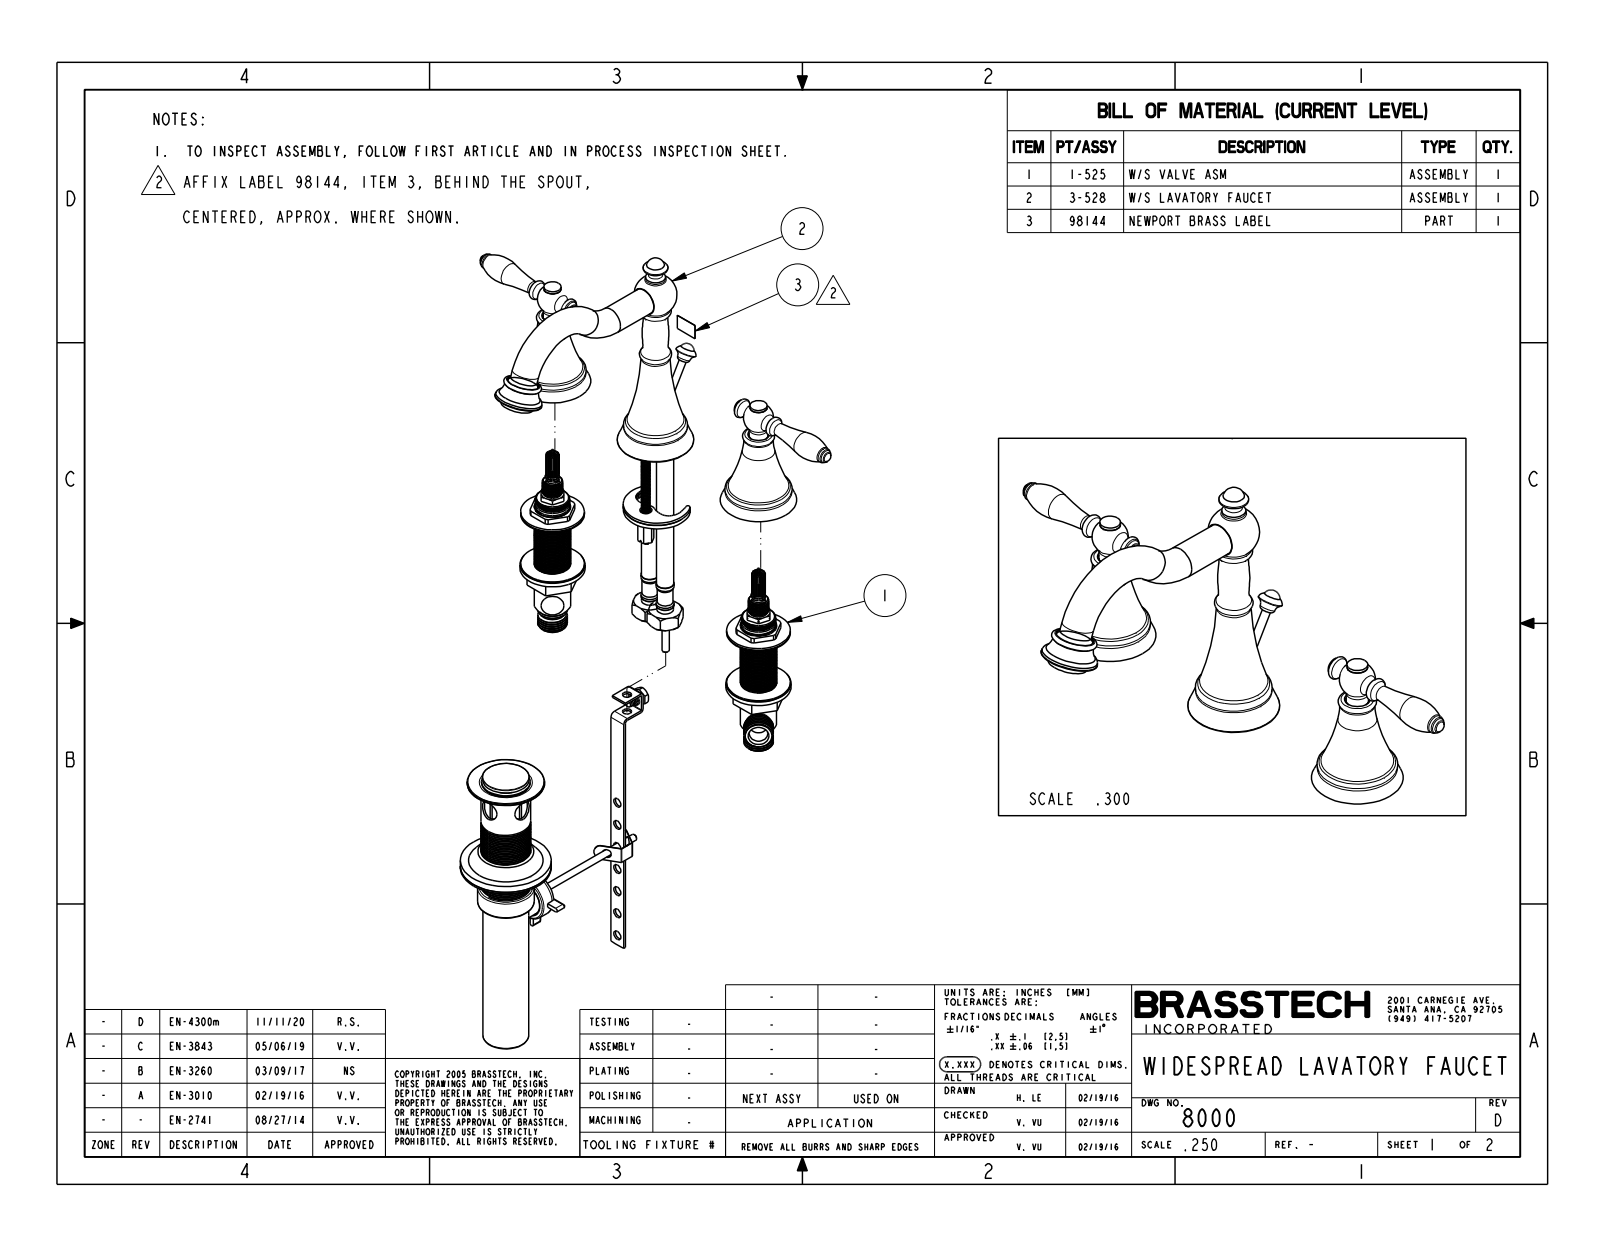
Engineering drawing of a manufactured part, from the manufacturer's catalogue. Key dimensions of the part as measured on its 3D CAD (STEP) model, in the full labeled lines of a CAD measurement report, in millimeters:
Part name (STEP PRODUCT): 8000
STEP written by: CREO PARAMETRIC BY PTC INC, 2018400 (CONFIG_CONTROL_DESIGN)
Units: millimetres
Bodies: 4 solids, 203 faces (8 planar, 16 cylindrical, 179 other)
Overall size (bounding box): 342.6 × 187.8 × 154.8
Volume: 249 400 mm³ · Surface area: 55 470 mm²
Round bosses / shafts (diameter × count): ⌀19 ×2, ⌀13 ×2, ⌀12 ×2, ⌀14 ×1, ⌀5 ×1
Main face-to-face distances: 55.9, 18
